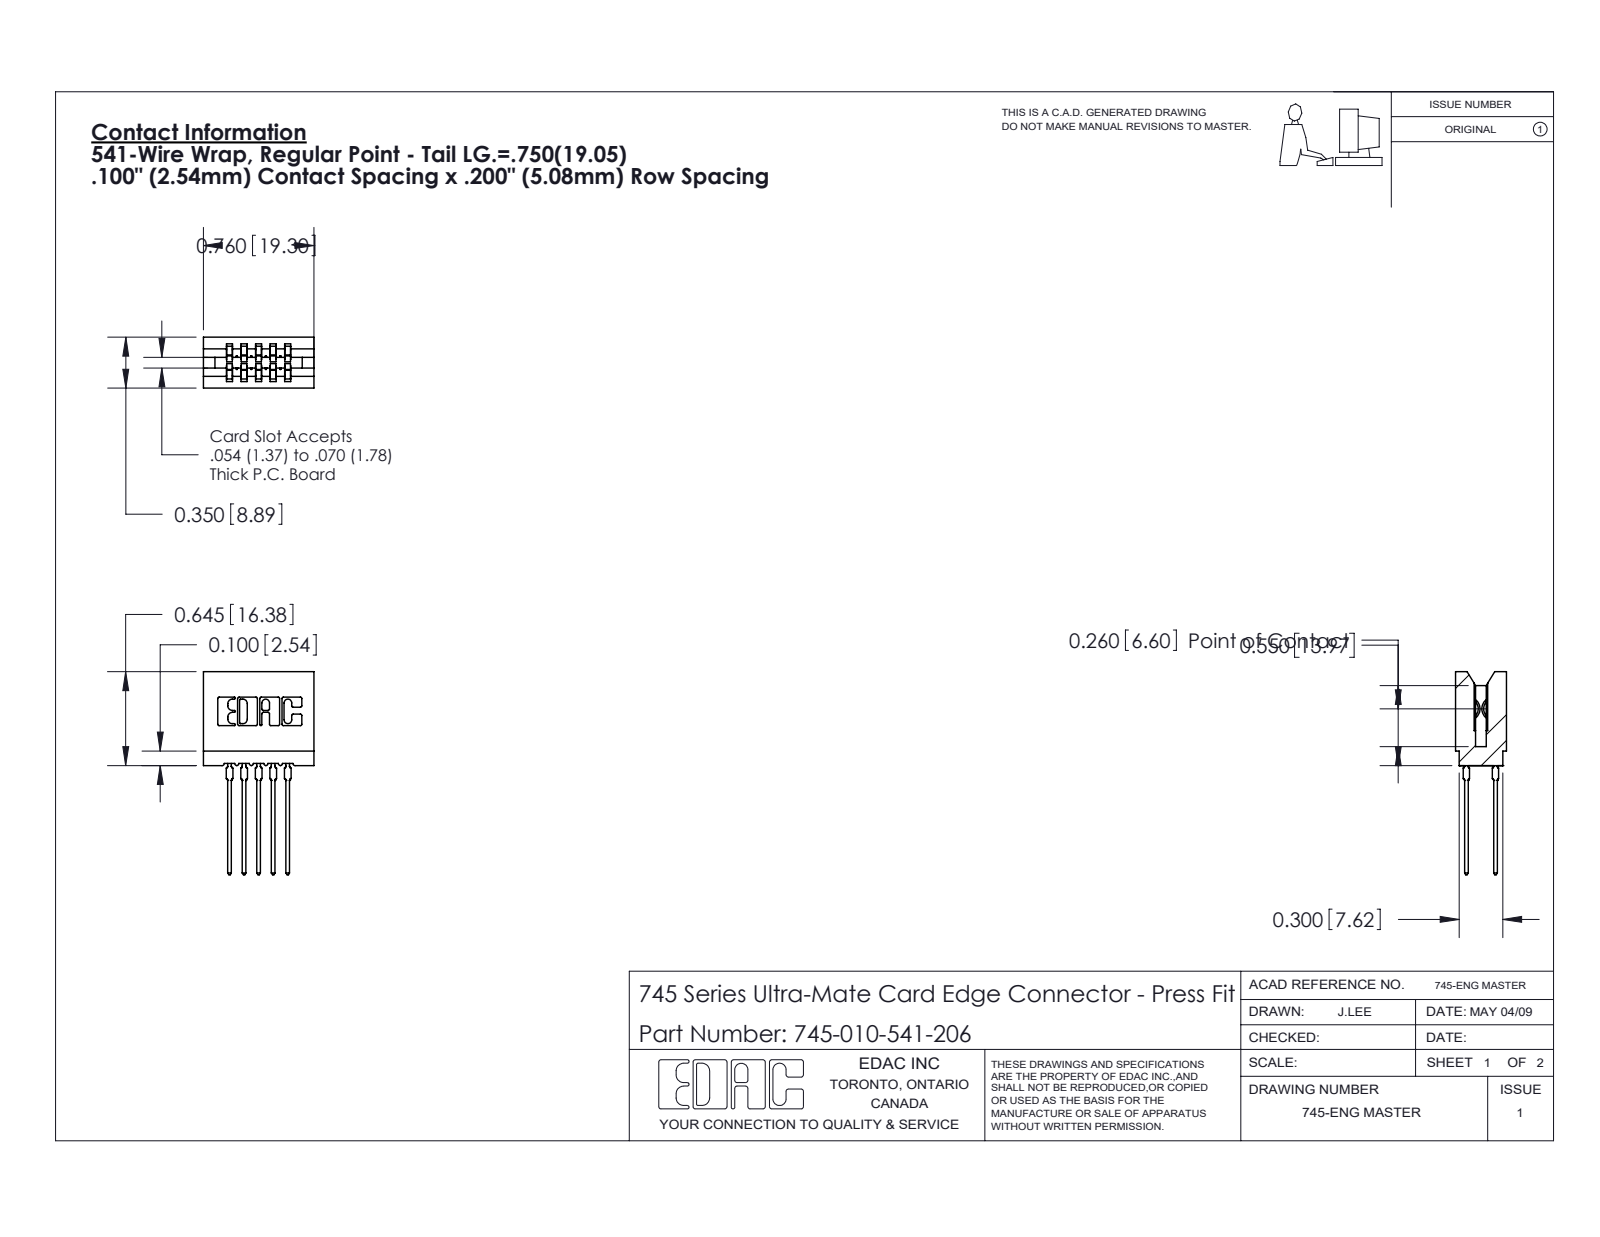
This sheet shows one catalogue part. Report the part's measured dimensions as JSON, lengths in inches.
{"part_name": "745-010-541-206; 745 Part_Insulator Option - 06; 745-292-001_541", "step_written_by": "SolidWorks 2020 (CONFIG_CONTROL_DESIGN)", "units": "inches", "bodies": {"solids": 11, "faces": 991, "planar": 516, "cylindrical": 215, "other": 260}, "overall_size": [1.396, 0.76, 0.35], "volume_in3": 0.121, "surface_area_in2": 5.288, "partial_cylinders_radius": [[0.01, 22], [0.021, 20], [0.015, 10], [0.005, 8], [0.011, 8], [0.007, 6], [0.031, 6], [0.026, 3]], "face_to_face_distances": [0.1, 0.2, 0.042, 0.3, 0.142, 0.058, 0.063, 0.287, 0.35, 0.242]}
